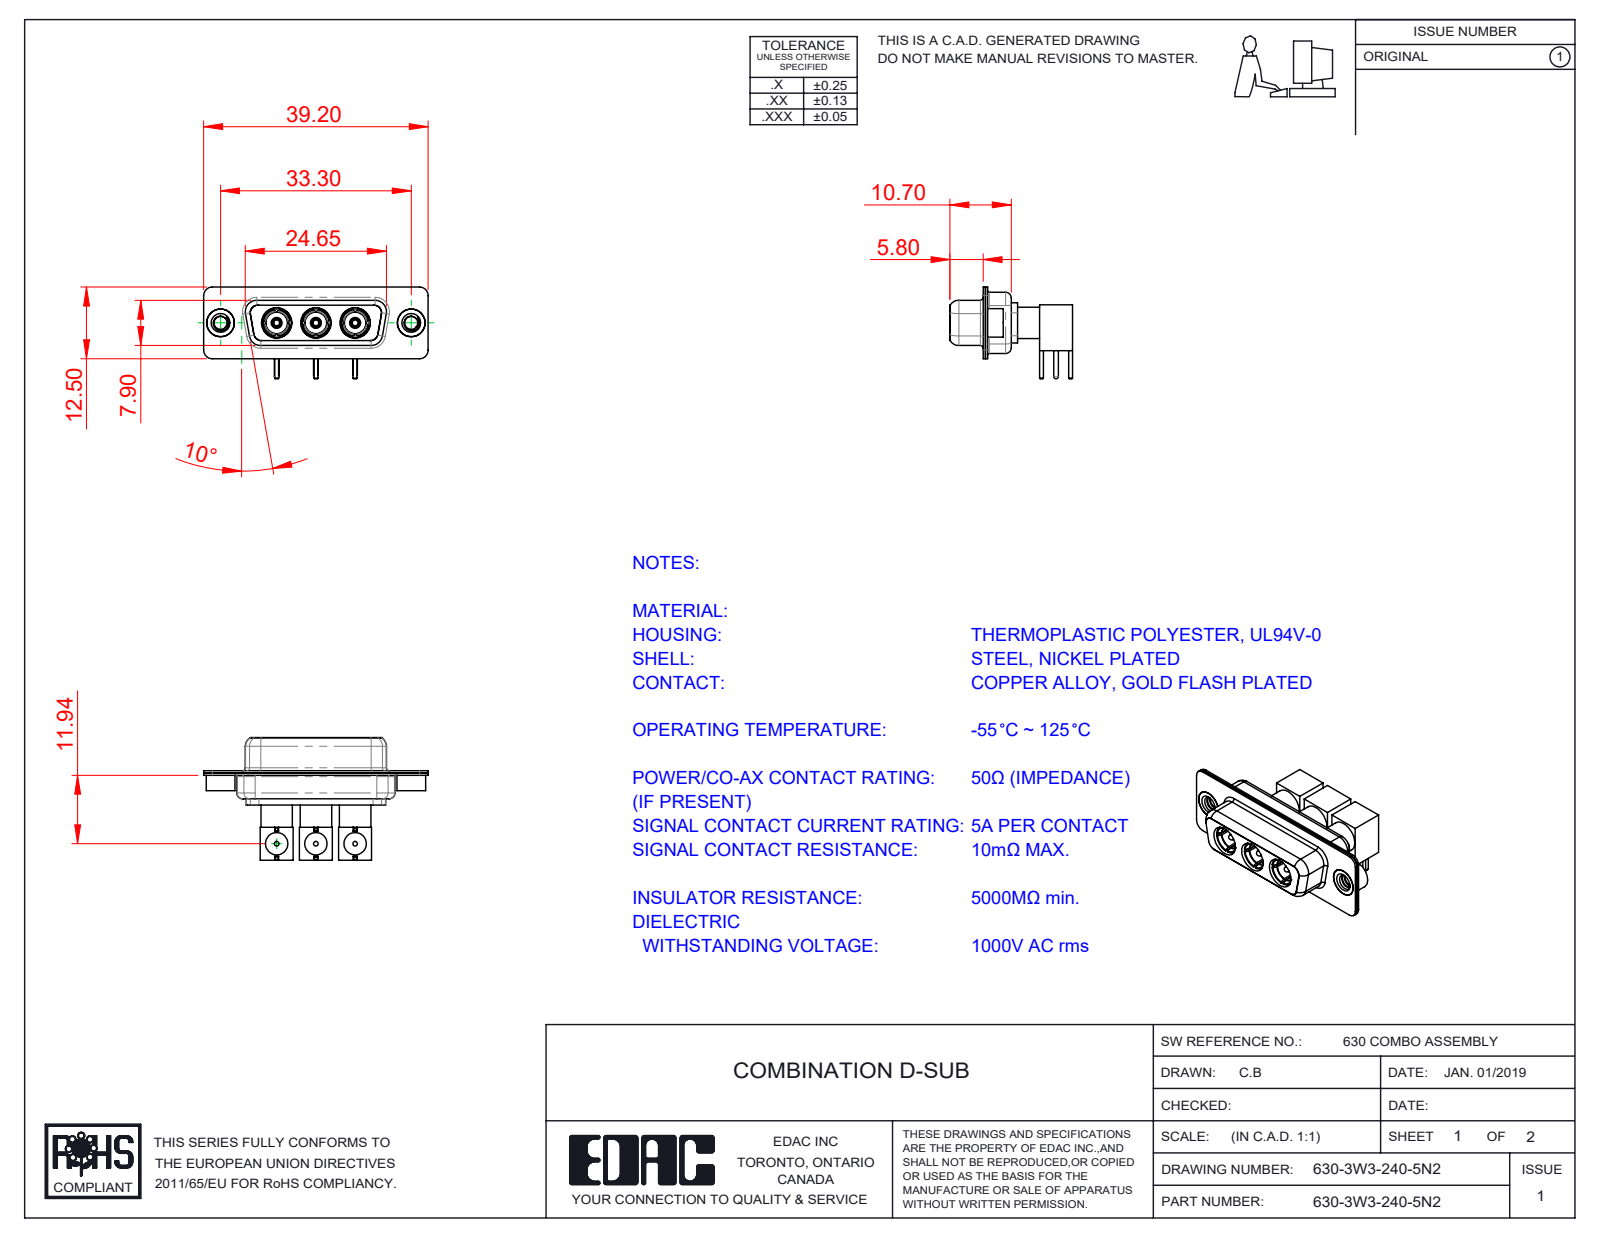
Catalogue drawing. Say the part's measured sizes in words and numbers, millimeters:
The part is named "Locking Collar; Co-Ax Plug_RA PC Tail; Insulator Pin_Straight PC Tail; RA Back Shell (+8 more)". Its 3-D file was written by "SolidWorks 2020 (CONFIG_CONTROL_DESIGN)". It is 23 solids with 783 faces: 268 planar, 332 cylindrical and 183 other. Overall it measures 39.2 by 21.41 by 16 millimeters. Its volume is 3 140 cubic millimeters and its surface area 7 790 square millimeters. Round holes: 5 of diameter 4.85, 3 of diameter 0.8, 3 of diameter 1.1, 3 of diameter 1.5, 3 of diameter 2.83, 3 of diameter 3.1, 3 of diameter 3.3, 3 of diameter 3.9, 3 of diameter 3.92, 3 of diameter 4.1, 3 of diameter 5.3, 2 of diameter 2.26. Round bosses or shafts: 5 of diameter 5, 3 of diameter 5.5, 3 of diameter 5.2, 3 of diameter 4.75, 3 of diameter 4.15, 3 of diameter 4, 3 of diameter 3.76, 3 of diameter 3.75. Partial cylindrical surfaces (rounded edges, fillets, slot ends): 16 of radius 1.5, 12 of radius 1.35, 12 of radius 2, 8 of radius 1.6, 4 of radius 0.25, 4 of radius 0.5, 4 of radius 0.6, 4 of radius 0.65. The main face-to-face distances are 0.4, 1.8, 1.4, 0.45, 8.45, 0.8, 8.9, 5.75, 1.85, 6.85. The hole center spacings are 6.85, 9.8, 13.7, 16.65, 23.5, 33.3.
